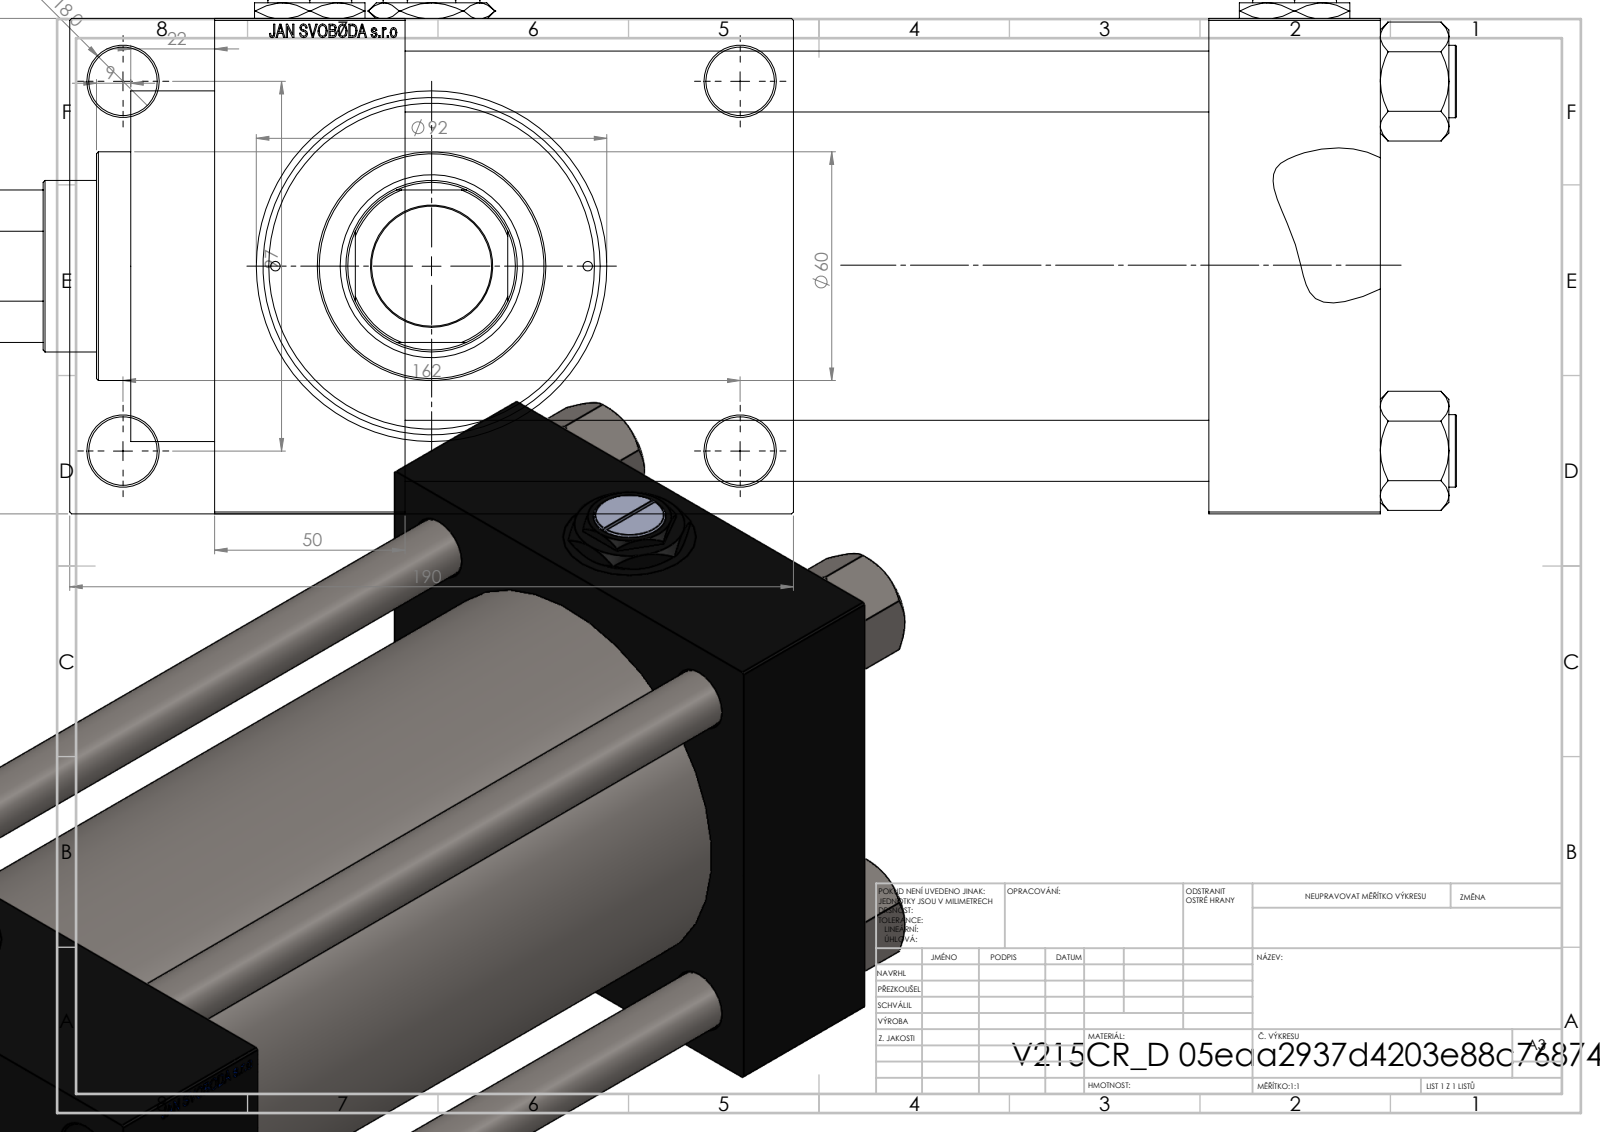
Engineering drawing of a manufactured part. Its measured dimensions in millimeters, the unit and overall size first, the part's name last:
Units: millimetres
Overall size (bounding box): 383 × 190 × 137
Round holes (diameter × count): ⌀16 ×4, ⌀18 ×4, ⌀2.5 ×2, ⌀7 ×2, ⌀26.44 ×2, ⌀35 ×2, ⌀31.5 ×1, ⌀45 ×1, ⌀48 ×1, ⌀76 ×1, ⌀85.5 ×1, ⌀100 ×1
Round bosses / shafts (diameter × count): ⌀19 ×4, ⌀106 ×1, ⌀92 ×1, ⌀60 ×1
Partial cylindrical surfaces — rounded edges, fillets, slot ends (radius × count): R22 ×1
Main face-to-face distances: 130, 45, 160, 256, 211, 306, 261, 50, 30, 190
Hole centre spacings: 32.55, 49.02, 62.87, 68.52, 94.41, 96.9, 101.73, 102.27
Volume: 3 063 000 mm³ · Surface area: 497 702 mm²
Bodies: 13 solids, 1261 faces (595 planar, 104 cylindrical, 562 other)
Part name (STEP PRODUCT): V215CR_D_Body; V215CR_D_TYCINKA; NUT_M5_D; V215_VC_A (+2 more)
STEP written by: SolidWorks 2019 (CONFIG_CONTROL_DESIGN)
